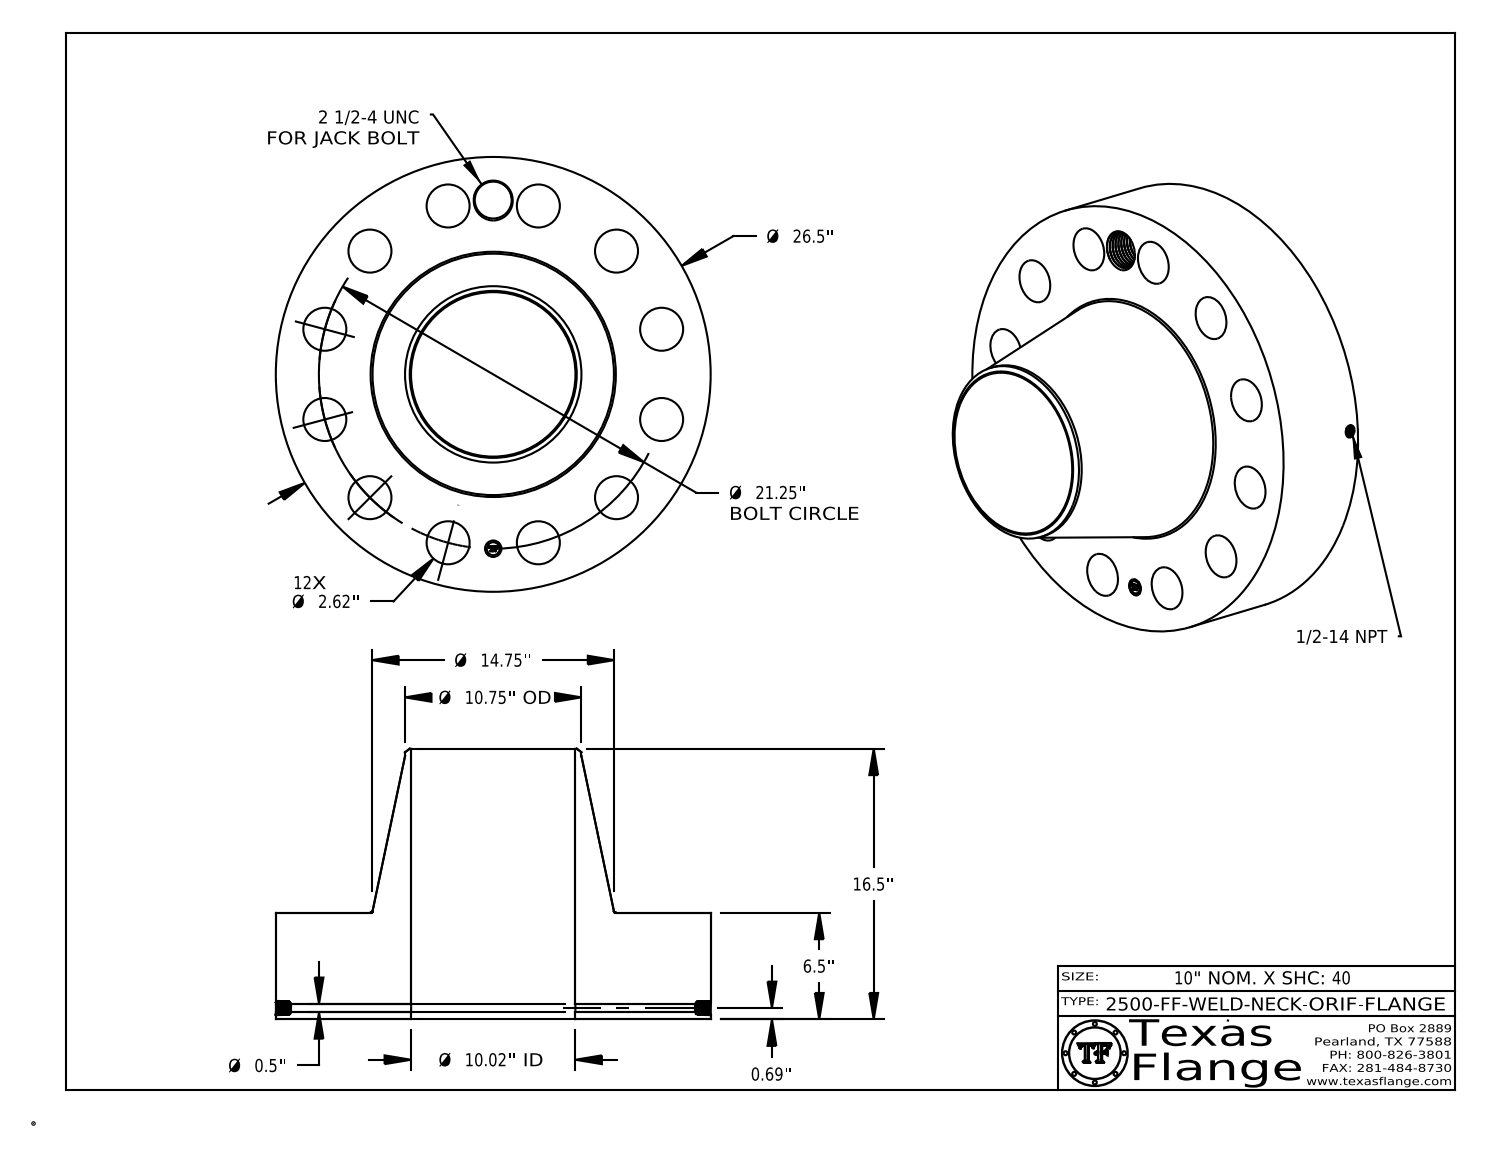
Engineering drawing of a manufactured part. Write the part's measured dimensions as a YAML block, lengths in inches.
part_name: "2500-FF-WELD-NECK"
step_written_by: "CATIA V5 STEP AP214 (AUTOMOTIVE_DESIGN)"
units: inches
bodies: {solids: 1, faces: 840, planar: 368, cylindrical: 122, other: 350}
overall_size: [26.5, 26.5, 16.5]
volume: 3100
surface_area: 2927
round_holes:
  - {diameter: 2.62, count: 12}
  - {diameter: 0.5, count: 1}
  - {diameter: 0.672, count: 1}
  - {diameter: 1, count: 1}
  - {diameter: 2.25, count: 1}
  - {diameter: 10.02, count: 1}
round_bosses_or_shafts:
  - {diameter: 0.061, count: 8}
  - {diameter: 26.5, count: 1}
  - {diameter: 10.75, count: 1}
  - {diameter: 0.788, count: 1}
face_to_face_distances: [6.5, 16.5, 10, 0.015, 6.485, 10.015, 0.298, 0.292, 0.054, 0.248]
hole_center_spacings: [10.625, 5.5, 15.026, 18.403, 20.526, 10.625, 21.25, 2.774]
